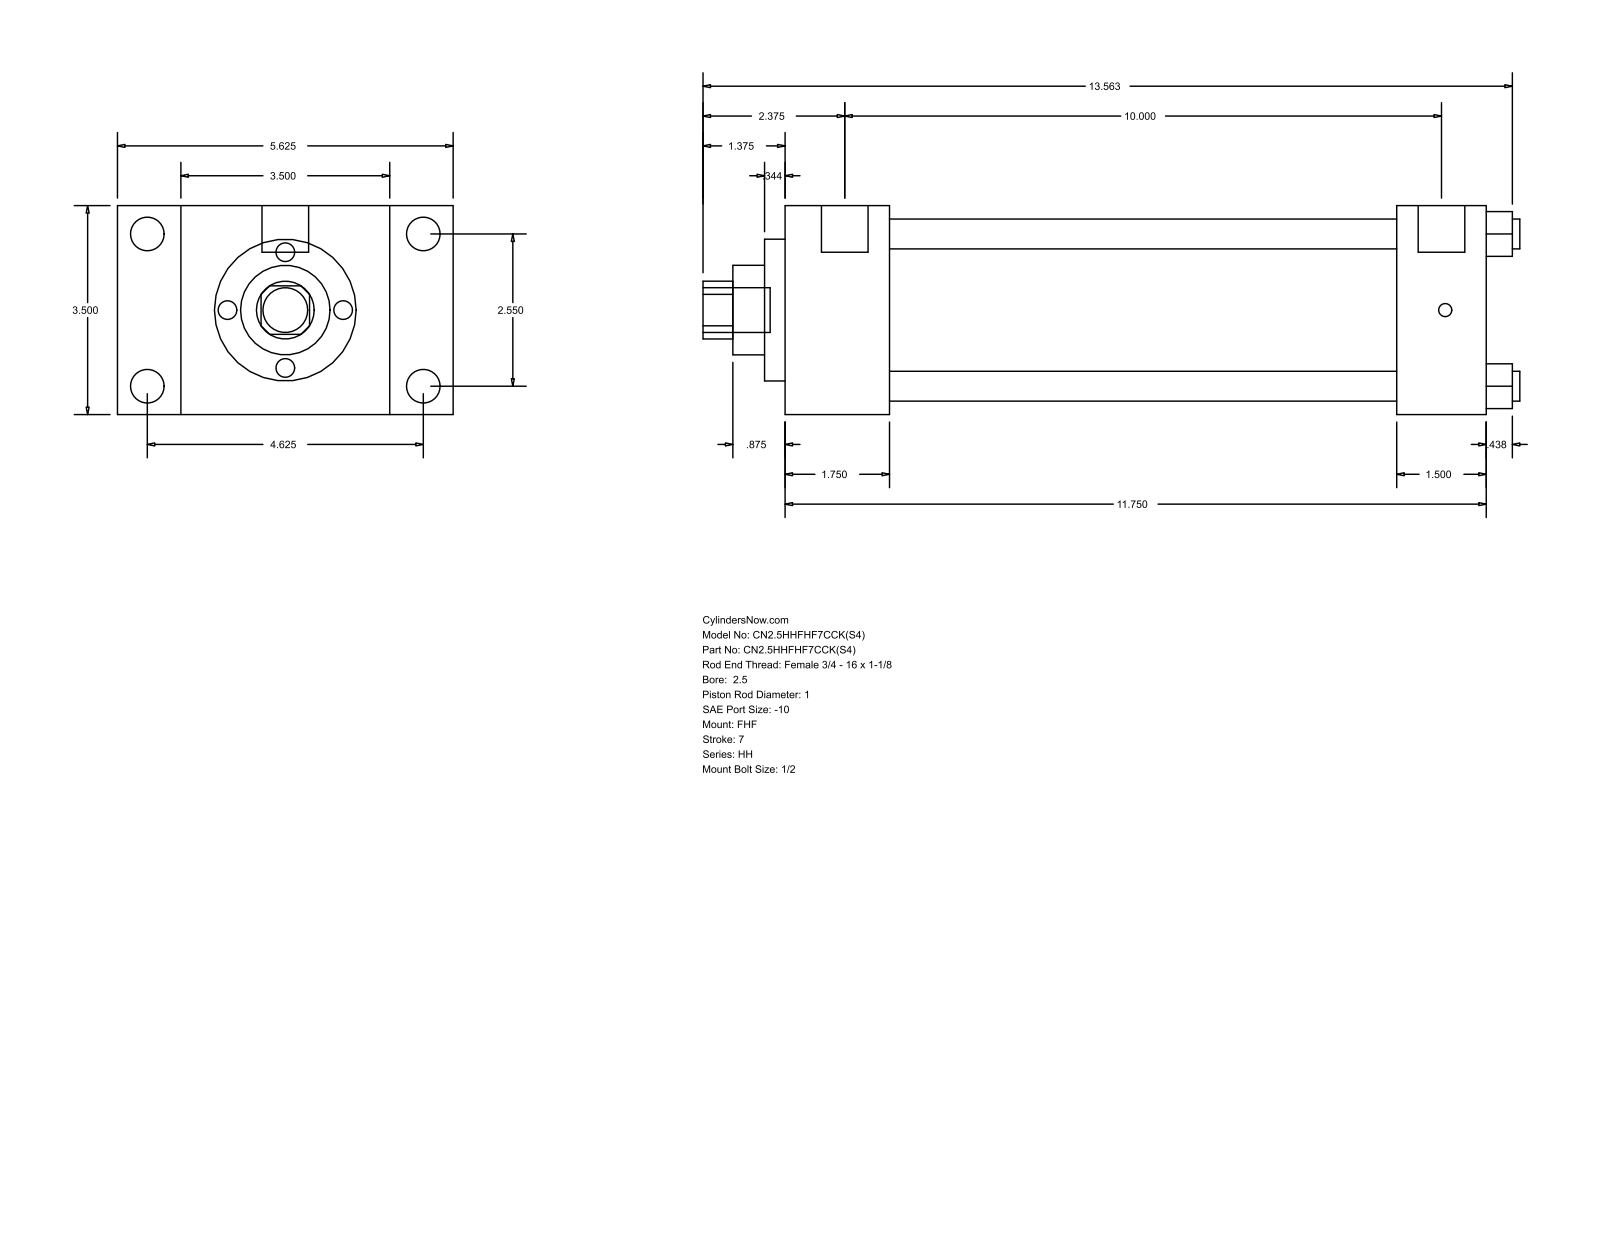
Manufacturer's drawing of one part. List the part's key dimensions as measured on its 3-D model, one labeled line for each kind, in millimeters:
Part name (STEP PRODUCT): HH_FHF__0250_1
STEP written by: GSSL Pune (CONFIG_CONTROL_DESIGN)
Units: millimetres
Bodies: 0 solids, 90 faces (61 planar, 29 cylindrical, 0 other)
Overall size (bounding box): 347.66 × 142.88 × 88.9
Round holes (diameter × count): ⌀12.7 ×4, ⌀25.4 ×1, ⌀38.1 ×1, ⌀60.33 ×1, ⌀73.03 ×1
Round bosses / shafts (diameter × count): ⌀14.3 ×4, ⌀5.56 ×4, ⌀19.84 ×2, ⌀19.05 ×1
Partial cylindrical surfaces — rounded edges, fillets, slot ends (radius × count): R12.29 ×1
Main face-to-face distances: 88.9, 44.46, 26.99, 115.89, 298.46, 254, 142.88, 260.35, 215.89, 38.11
Hole centre spacings: 45.79, 64.76, 91.58
